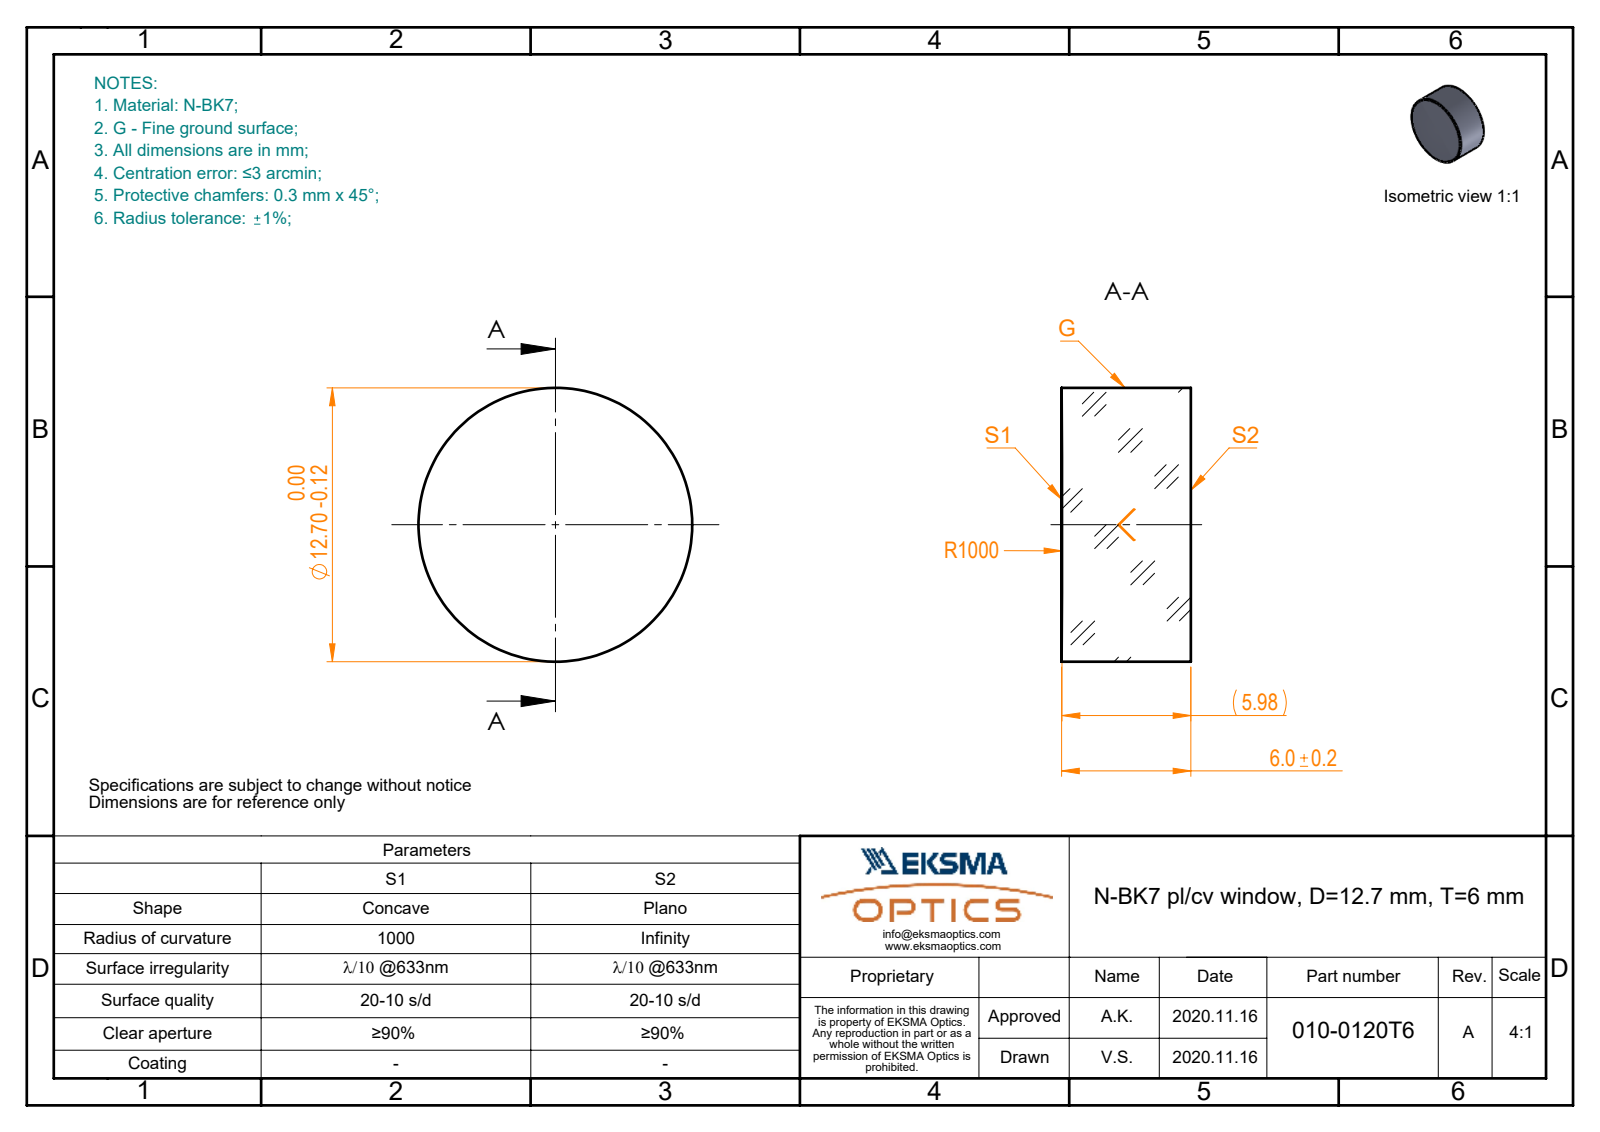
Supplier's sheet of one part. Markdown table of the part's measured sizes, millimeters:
| quantity | value |
| --- | --- |
| part name | 010-0120T6_N-BK7_PCV_window |
| STEP written by | SolidWorks 2019 (CONFIG_CONTROL_DESIGN) |
| units | millimeters |
| bodies | 1 solid, 5 faces (1 planar, 2 cylindrical, 2 other) |
| overall size | 12.7 × 12.7 × 6 |
| volume | 759 mm³ |
| surface area | 493 mm² |
| round bosses / shafts (diameter × count) | 12.7 × 1 |
